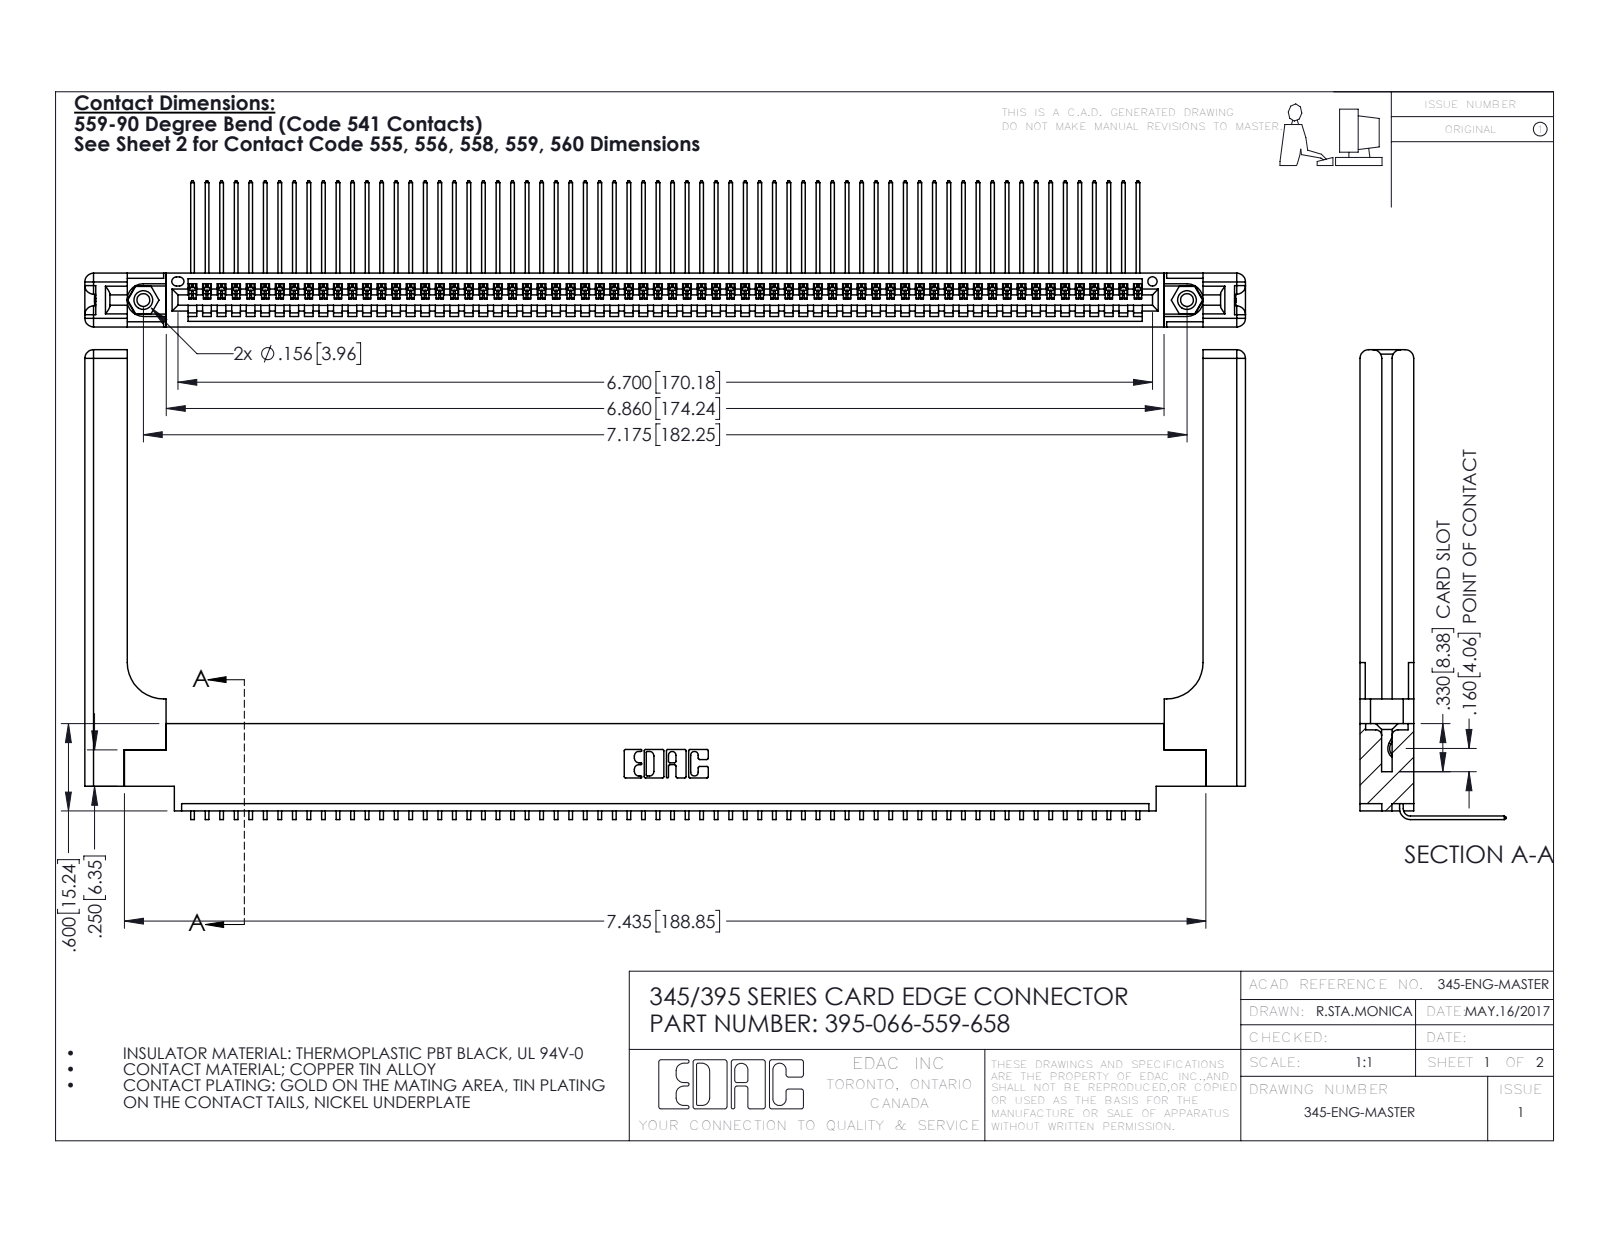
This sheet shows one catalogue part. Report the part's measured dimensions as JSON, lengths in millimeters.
{"part_name": "395-066-559-658; 345 Part_0.170 Offset - 0.156 Dia-TH; 345-220-058_345-220-058; 345-250-001_345-250-001-102 (+1 more)", "step_written_by": "SolidWorks 2016 (CONFIG_CONTROL_DESIGN)", "units": "millimeters", "bodies": {"solids": 71, "faces": 4346, "planar": 3004, "cylindrical": 1282, "other": 60}, "overall_size": [202.7, 82, 25.5], "volume_mm3": 28050, "surface_area_mm2": 33030, "round_holes": [[2.3, 2], [3.2, 2], [4, 2], [1.6, 1]], "round_bosses_or_shafts": [[3.9, 2]], "partial_cylinders_radius": [[0.2, 132], [0.3, 22], [1.5, 16], [0.2, 6], [0.8, 6], [0.7, 3], [0.8, 2], [0.8, 2]], "face_to_face_distances": [1.8, 9.4, 7.6, 2.5, 6.9, 0.6, 5.1, 5.7, 3.8, 3.8], "hole_center_spacings": [6.9, 176.3, 182.2]}
